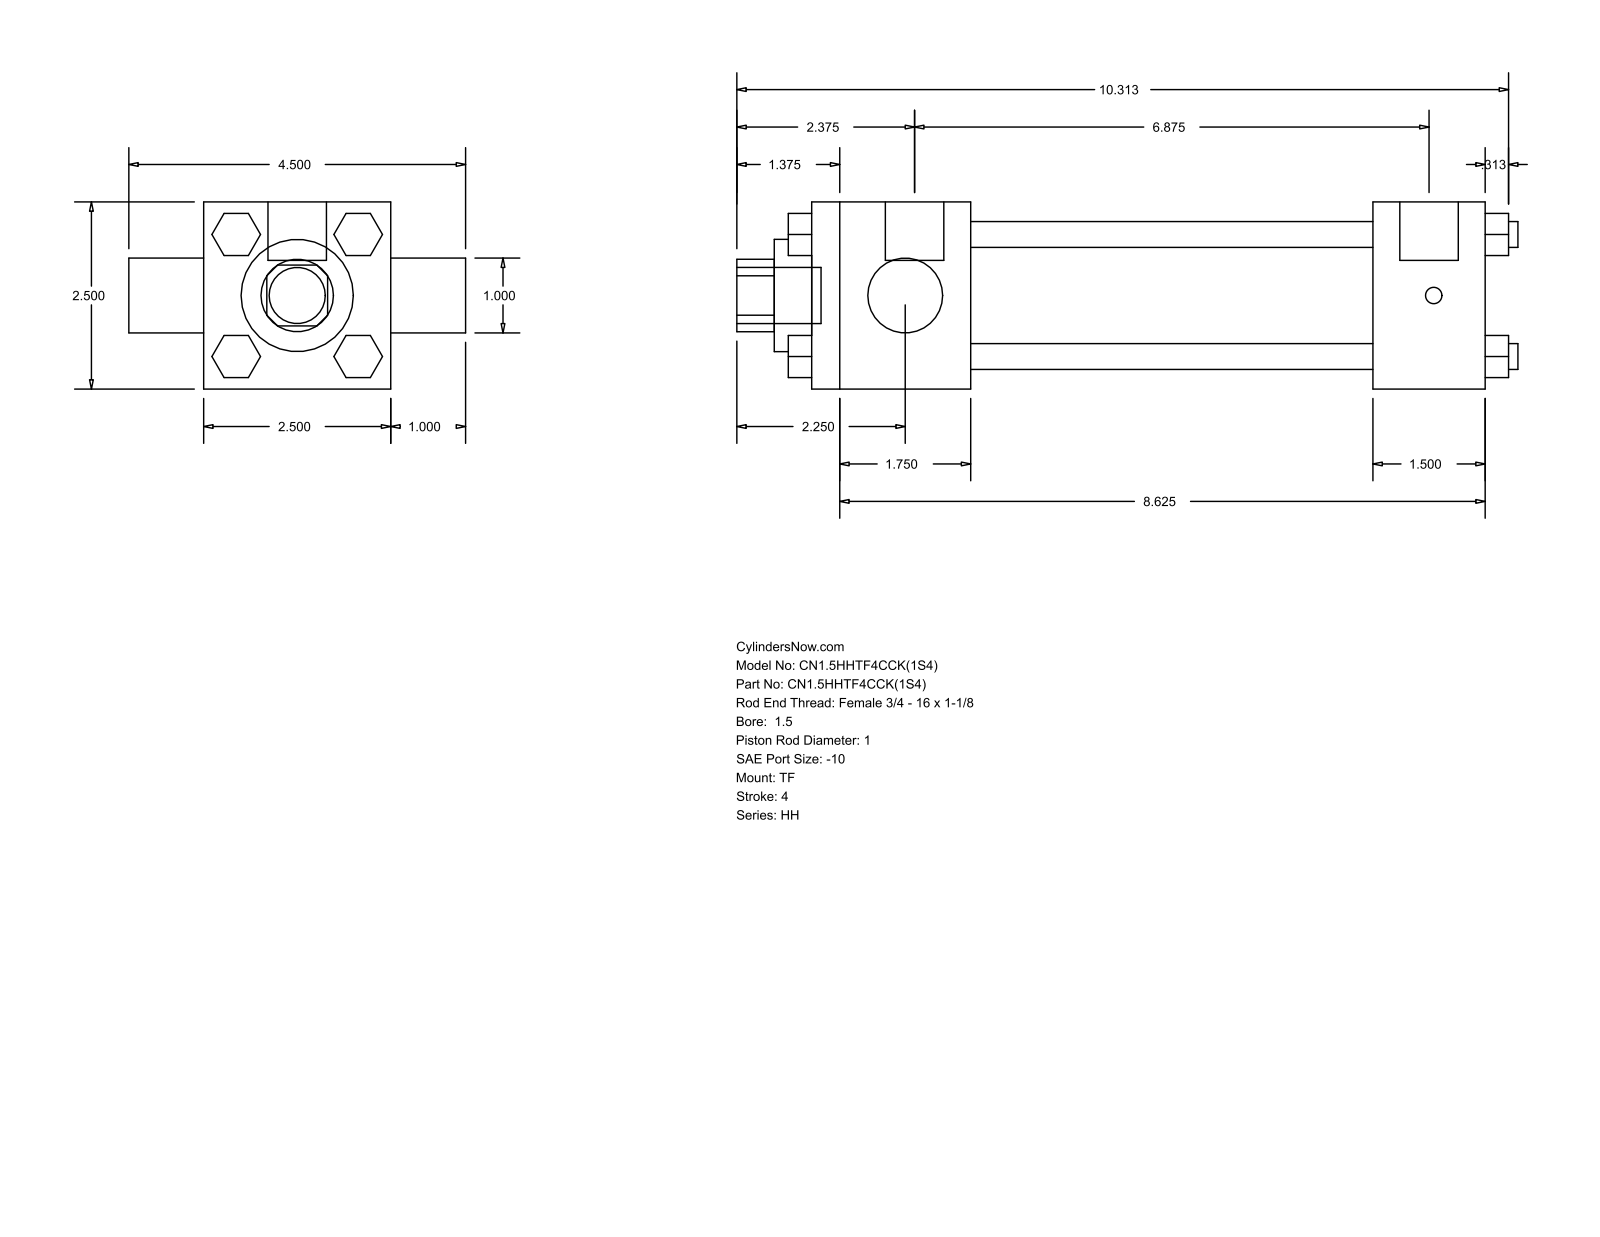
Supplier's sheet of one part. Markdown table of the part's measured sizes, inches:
| quantity | value |
| --- | --- |
| part name | HH_TF__0150_1 |
| STEP written by | GSSL Pune (CONFIG_CONTROL_DESIGN) |
| units | inches |
| bodies | 0 solids, 120 faces (92 planar, 28 cylindrical, 0 other) |
| overall size | 10.437 × 4.5 × 2.5 |
| round holes (diameter × count) | 1 × 2, 1.5 × 1, 1.75 × 1 |
| round bosses / shafts (diameter × count) | 0.345 × 4, 0.219 × 3, 0.781 × 2, 0.75 × 1 |
| partial cylindrical surfaces (radius × count) | 0.484 × 1 |
| main face-to-face distances | 2.5, 6.875, 5.375, 1.5, 2.125, 7.5, 9, 9.313, 1, 0.815 |
